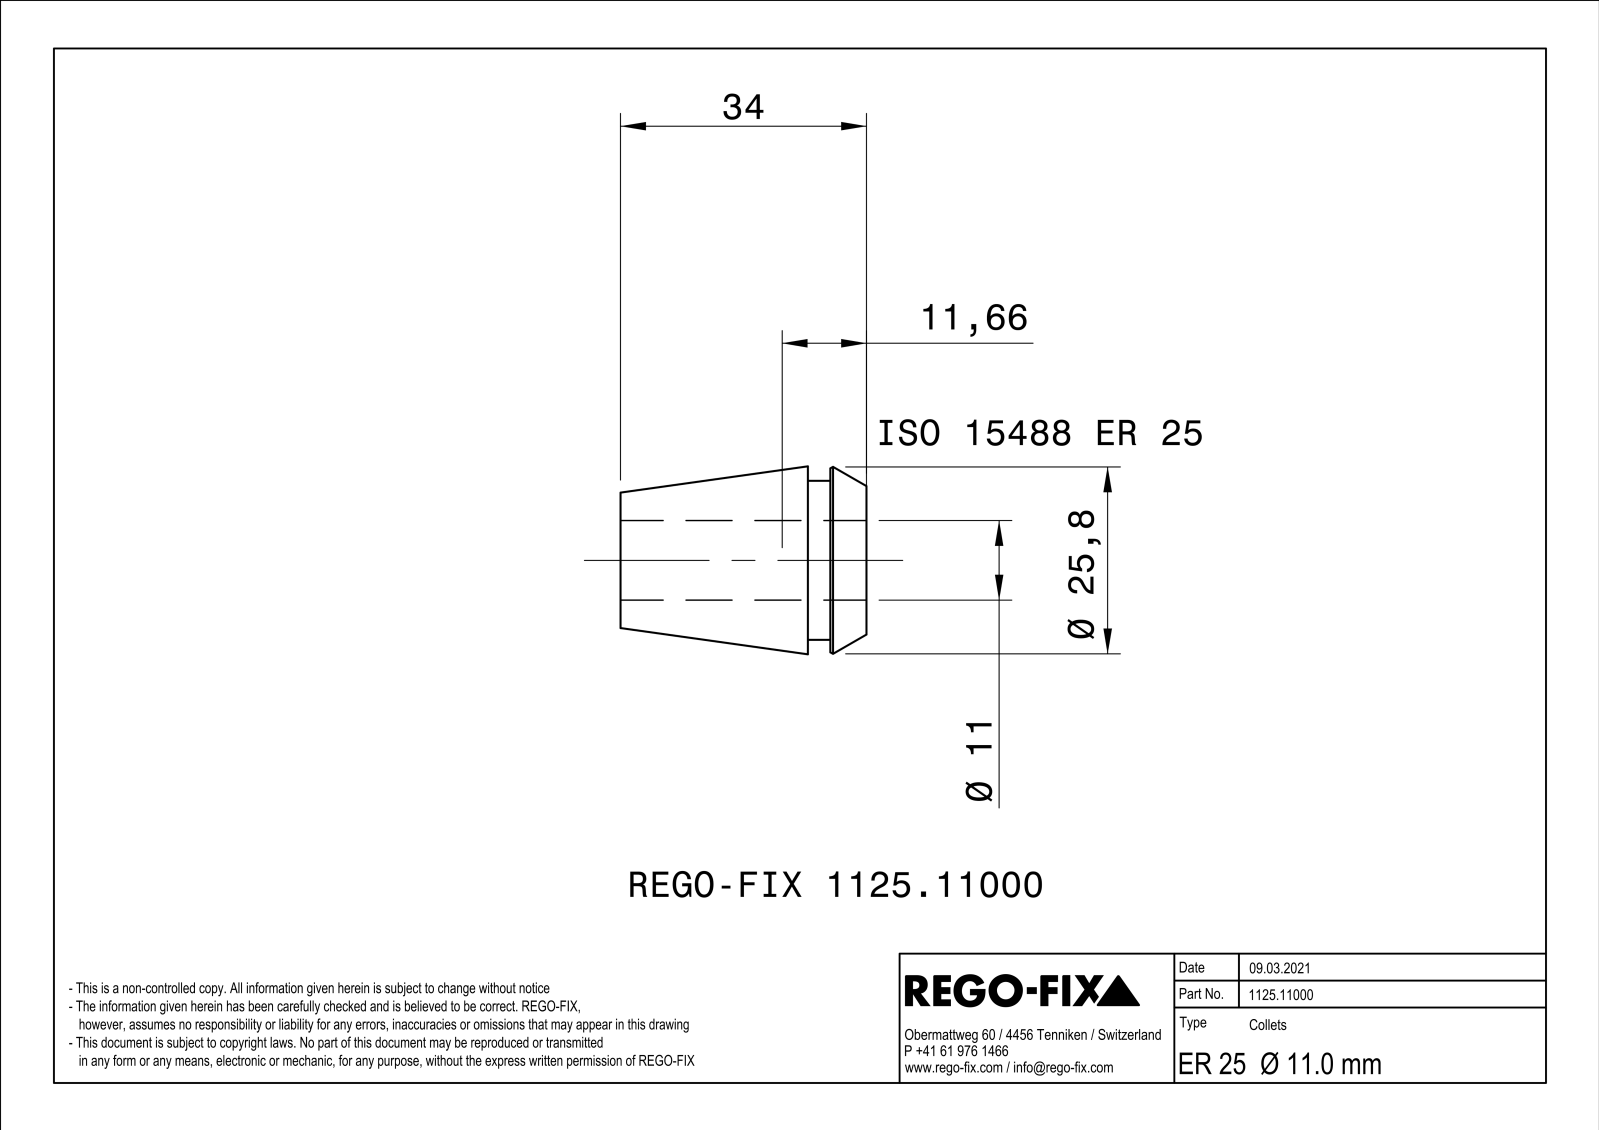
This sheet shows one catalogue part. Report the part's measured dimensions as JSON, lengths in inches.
{"part_name": "NOCUT", "step_written_by": "SIEMENS PLM Software Solid Edge ST10 (AUTOMOTIVE_DESIGN)", "units": "inches", "bodies": {"solids": 1, "faces": 177, "planar": 72, "cylindrical": 25, "other": 80}, "overall_size": [1.339, 1.023, 1.023], "volume_in3": 0.498, "surface_area_in2": 13.97, "round_holes": [[0.433, 1]], "round_bosses_or_shafts": [[0.866, 1]], "partial_cylinders_radius": [[0.016, 8]], "face_to_face_distances": [0.031, 1.339, 0.319, 1.02, 0.197, 0.122, 1.142]}
